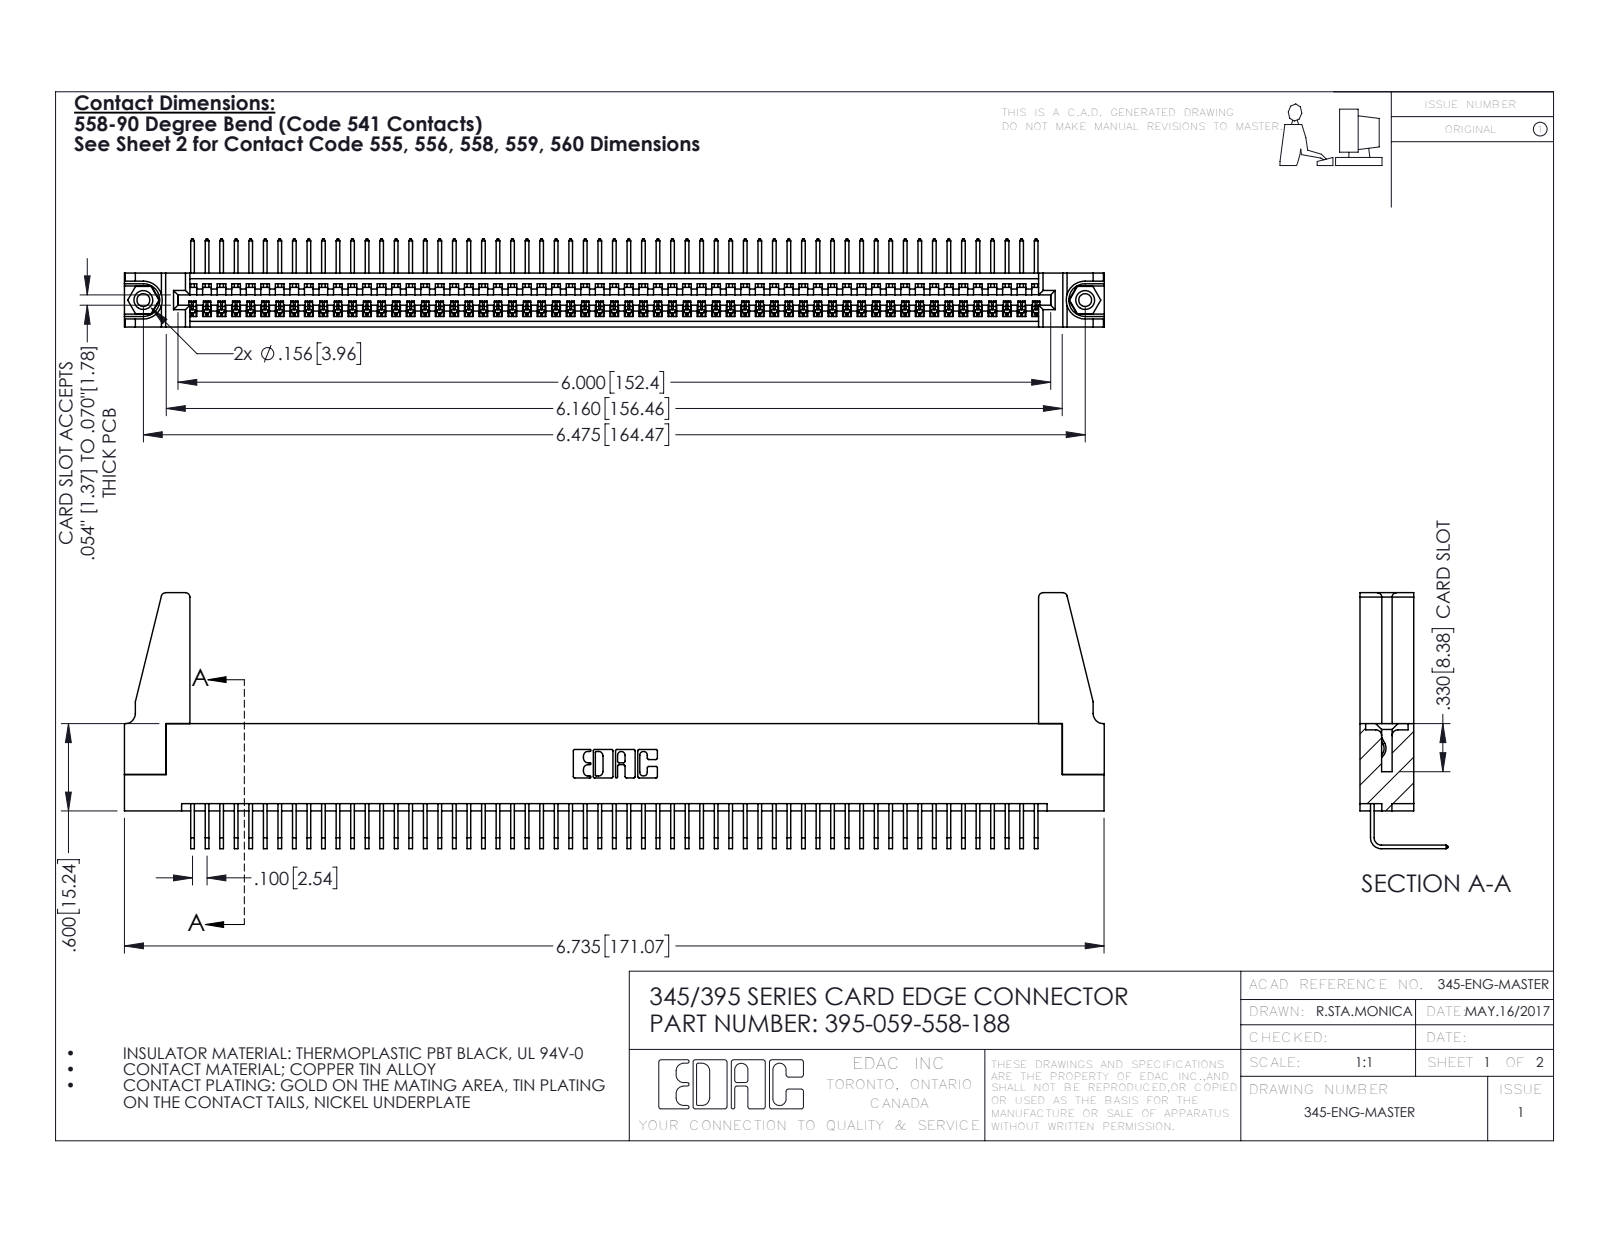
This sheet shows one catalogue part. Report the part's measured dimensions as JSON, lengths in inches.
{"part_name": "345-220-078_345-220-088; 395-059-558-188; 345-250-001_345-250-001-102; 345 Part_Flush Mounting Lugs - 0.156 Dia-TH (+1 more)", "step_written_by": "SolidWorks 2016 (CONFIG_CONTROL_DESIGN)", "units": "inches", "bodies": {"solids": 64, "faces": 3790, "planar": 2630, "cylindrical": 1144, "other": 16}, "overall_size": [6.736, 1.759, 0.605], "volume_in3": 1.211, "surface_area_in2": 41.16, "round_holes": [[0.089, 2], [0.125, 2], [0.156, 2], [0.064, 1]], "round_bosses_or_shafts": [[0.155, 2]], "partial_cylinders_radius": [[0.006, 118], [0.01, 22], [0.03, 8], [0.007, 6], [0.031, 6], [0.026, 3], [0.031, 2], [0.04, 2]], "face_to_face_distances": [0.072, 0.298, 0.37, 0.2, 0.098, 0.272, 0.025, 0.225, 0.149, 0.072], "hole_center_spacings": [0.27, 6.239, 6.475]}
